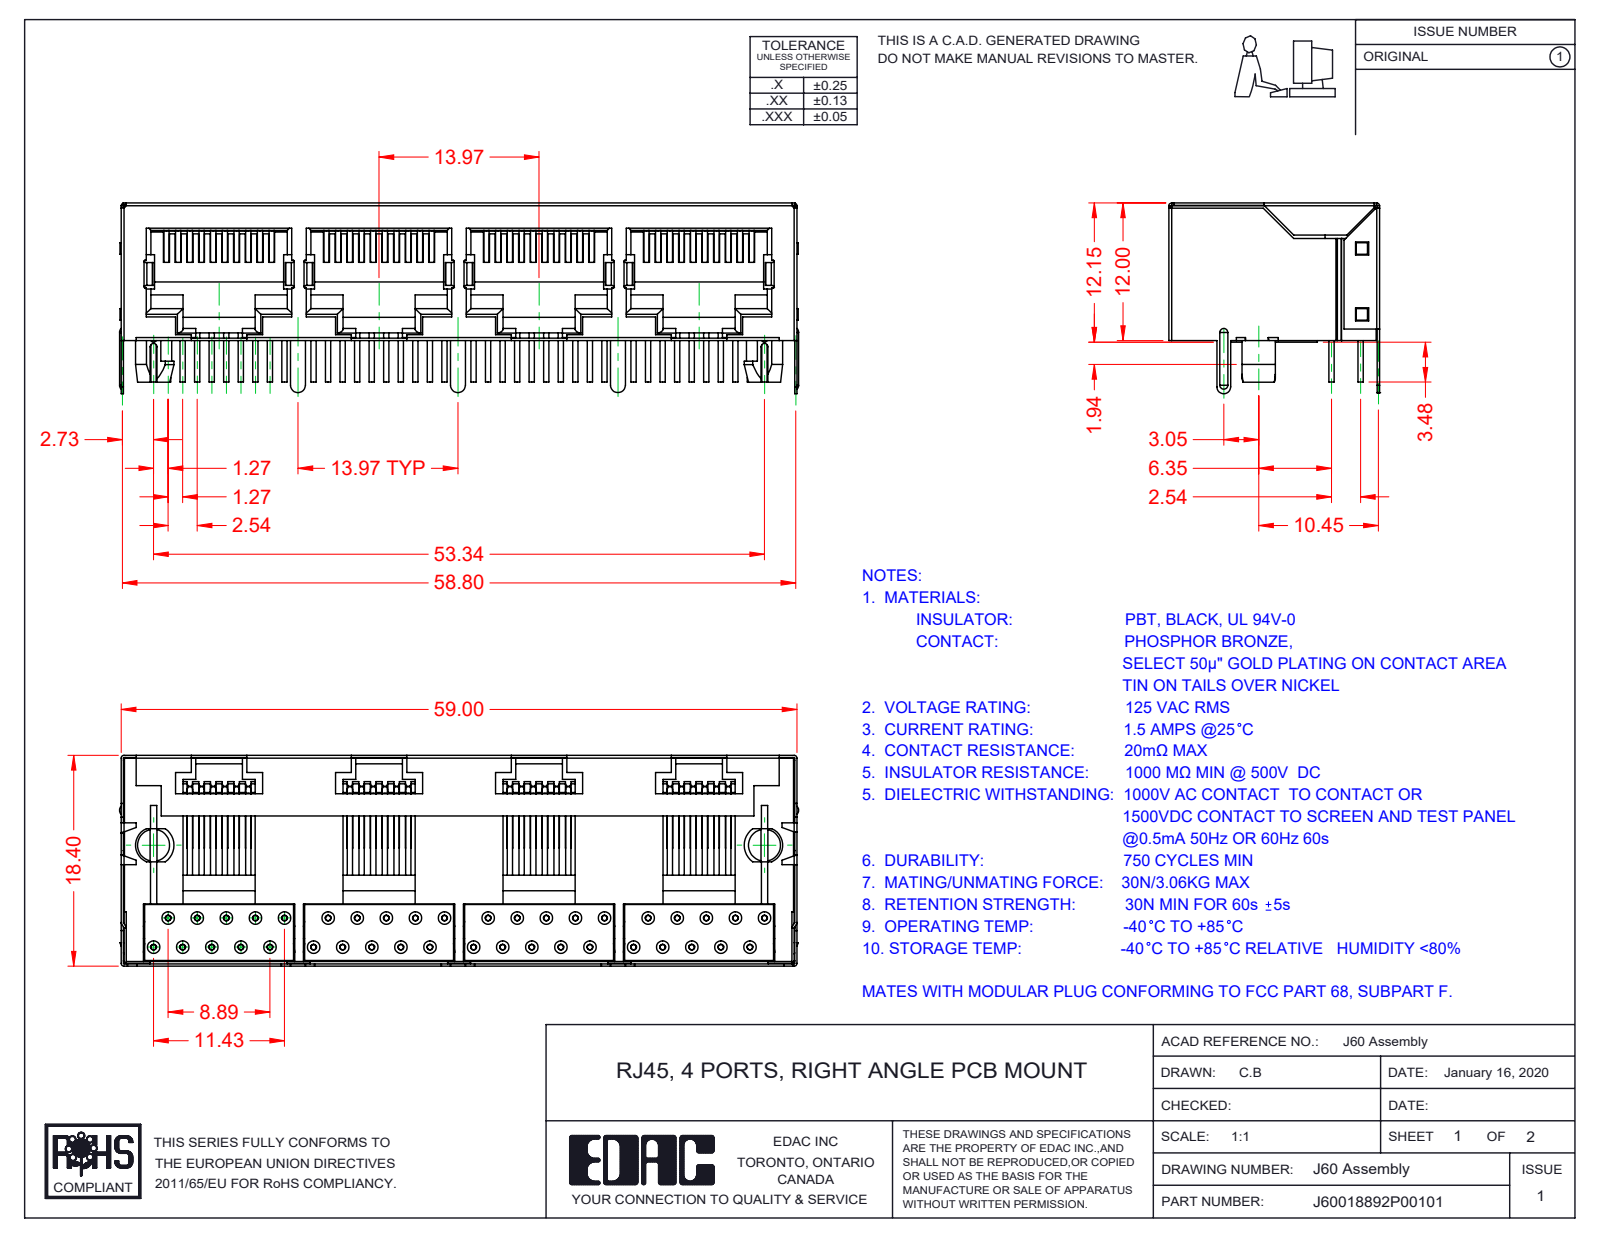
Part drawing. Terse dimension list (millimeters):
name: 60 Contacts_10P10C; 60 Shield; 60 Insulator; RJ60041192P00101
written by: SolidWorks 2016 (CONFIG_CONTROL_DESIGN)
unit: mm
bodies: 42 solids, 2674 faces (1505 planar, 763 cylindrical, 406 other)
size: 59.3 × 18.4 × 16.65
volume: 7 062 mm³; area: 18 987 mm²
holes: 40× ⌀0.5, 40× ⌀1.1
bosses: 120× ⌀0.46
rounds: 26× R0.3, 21× R0.25, 18× R0.5, 16× R0.1, 10× R0.21, 7× R0.8, 3× R0.65, 2× R0.28
face distances: 0.5, 11.75, 11.55, 13.97, 2.19, 5.38, 5.18, 4.88, 18.2, 11.5
hole spacings: 2.84, 2.54, 4.58, 13.97, 5.08, 12.95, 15.45, 11.43
